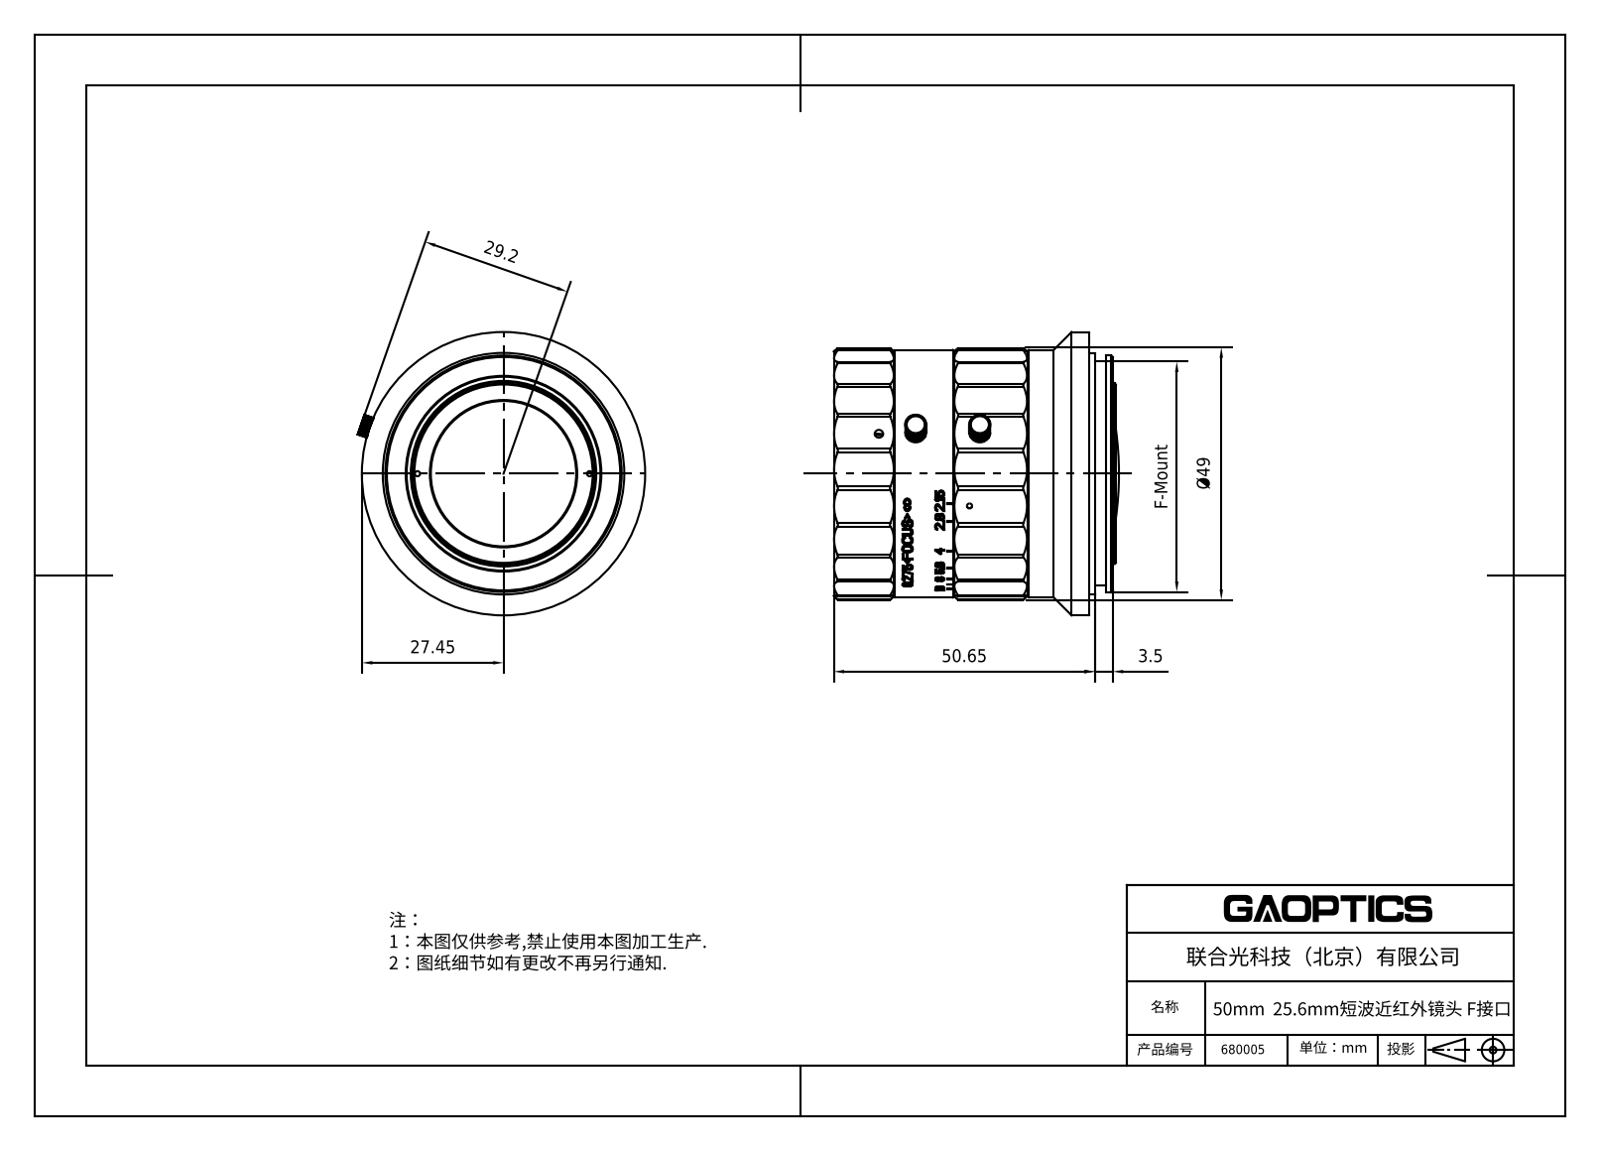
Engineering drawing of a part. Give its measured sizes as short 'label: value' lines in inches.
name: 680005
written by: SolidWorks 2020 (CONFIG_CONTROL_DESIGN)
unit: in
bodies: 0 solids, 2630 faces (1493 planar, 379 cylindrical, 758 other)
size: 2.195 × 2.179 × 2.164
holes: 2× ⌀0.039, 2× ⌀0.043, 1× ⌀1.11, 1× ⌀1.142, 1× ⌀1.15, 1× ⌀1.268, 1× ⌀1.315, 1× ⌀1.346, 1× ⌀1.425, 1× ⌀1.472, 1× ⌀1.495, 1× ⌀1.504
bosses: 5× ⌀0.063, 2× ⌀0.079, 2× ⌀0.059, 2× ⌀0.039, 1× ⌀2.164, 1× ⌀1.889, 1× ⌀1.85, 1× ⌀1.845
rounds: 30× R0.472, 26× R0.037, 4× R0.059, 2× R0.079, 1× R0.943
face distances: 1.014, 1.719, 0.704, 0.455, 0.559, 1.263, 0.186, 0.177, 0.632, 1.191
hole spacings: 0.657, 0.918, 0.659, 0.66, 0.944, 0.944, 1.315, 1.319
